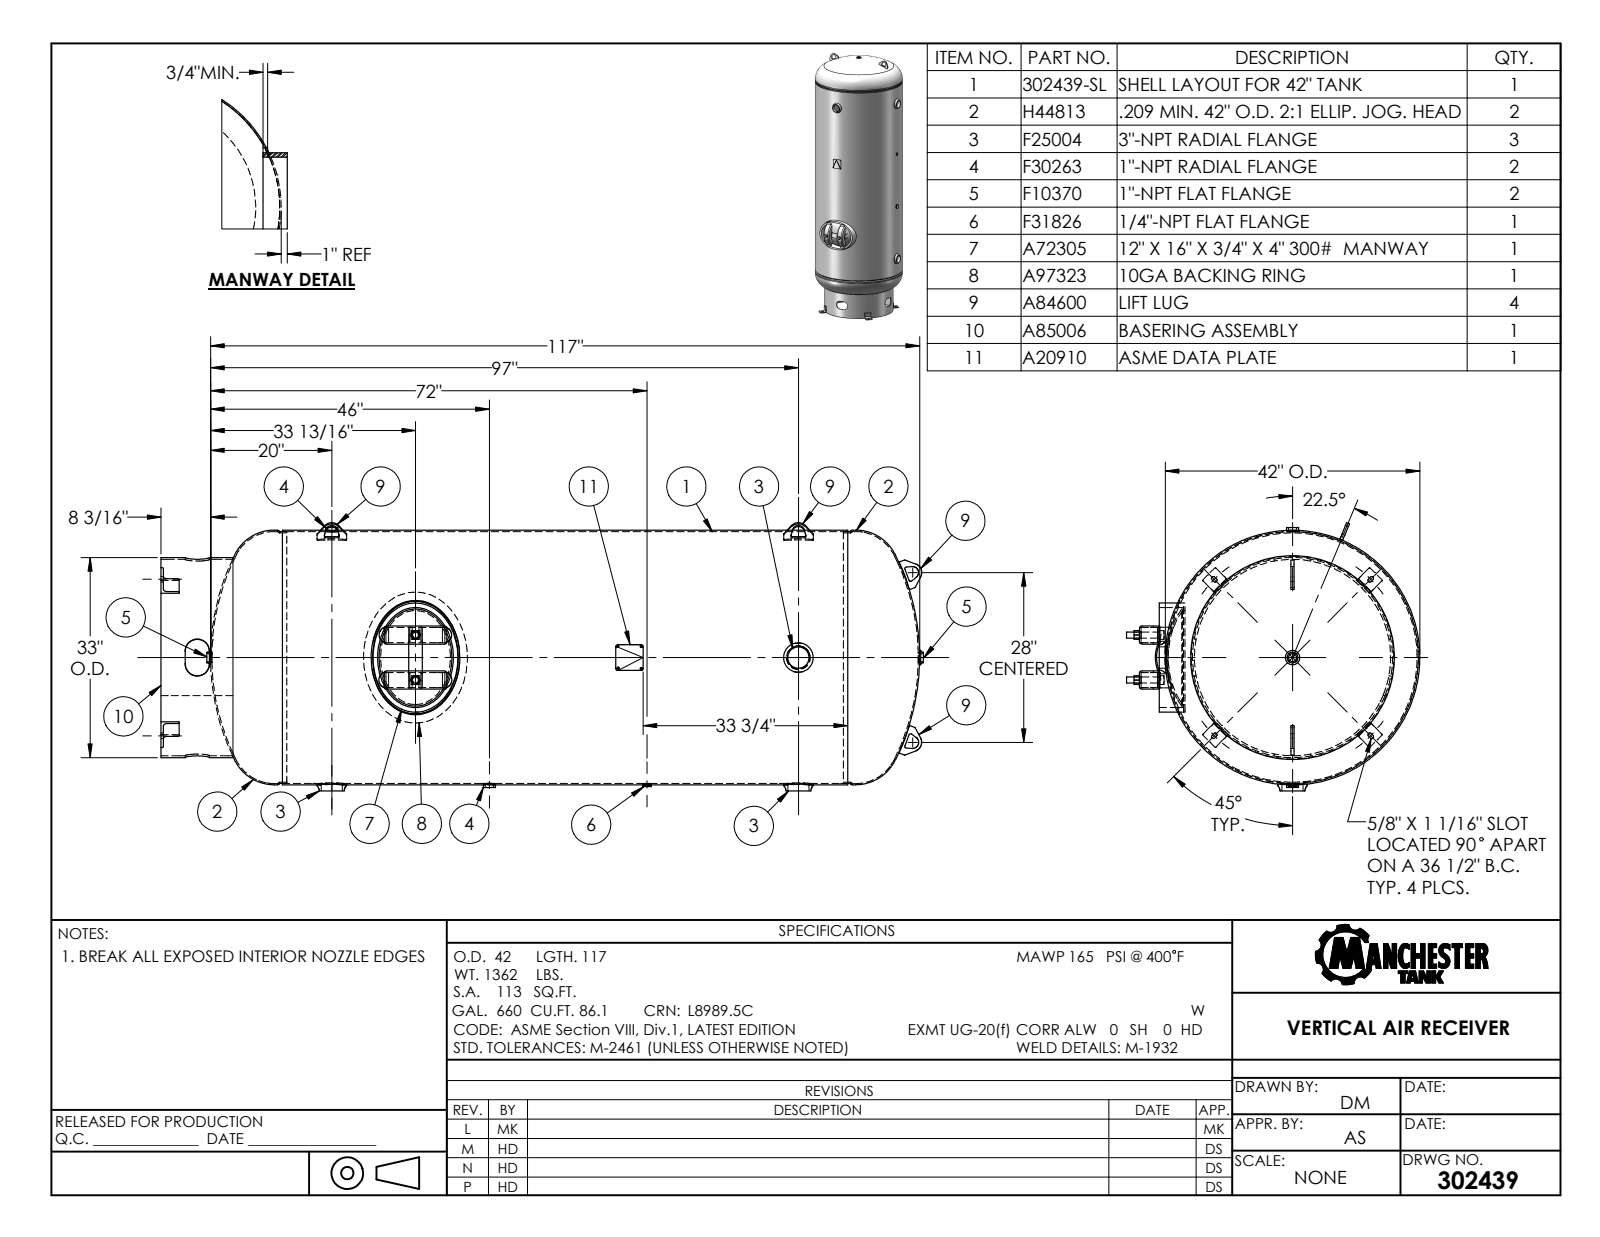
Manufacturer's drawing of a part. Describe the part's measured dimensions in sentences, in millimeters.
The part is named "302439". Its 3-D file was written by "SolidWorks 2011 (CONFIG_CONTROL_DESIGN)". It is 0 solids with 332 faces: 126 planar, 108 cylindrical and 98 other. Overall it measures 3217.9 by 1228.6 by 1112 millimeters. Round holes: 3 of diameter 88.9, 2 of diameter 33.4, 2 of diameter 34.9, 2 of diameter 34.9, 1 of diameter 13.7, 1 of diameter 33.4, 1 of diameter 822.4. Round bosses or shafts: 3 of diameter 123.8, 3 of diameter 60.3, 2 of diameter 25.4, 1 of diameter 1066.8, 1 of diameter 1054.1, 1 of diameter 838.2, 1 of diameter 44.5, 1 of diameter 38.1. Partial cylindrical surfaces (rounded edges, fillets, slot ends): 8 of radius 6.5, 6 of radius 7.9, 4 of radius 9.5, 4 of radius 14.3, 4 of radius 33.5, 4 of radius 50.8, 2 of radius 8, 1 of radius 150.3. The main face-to-face distances are 12.7, 108, 2879.3, 2368.6, 510.8, 76.2, 56.2, 132.4, 188.5, 457.2. The hole center spacings are 608.8, 660.4, 1955.8, 635, 711.2, 1295.4, 1320.8.
